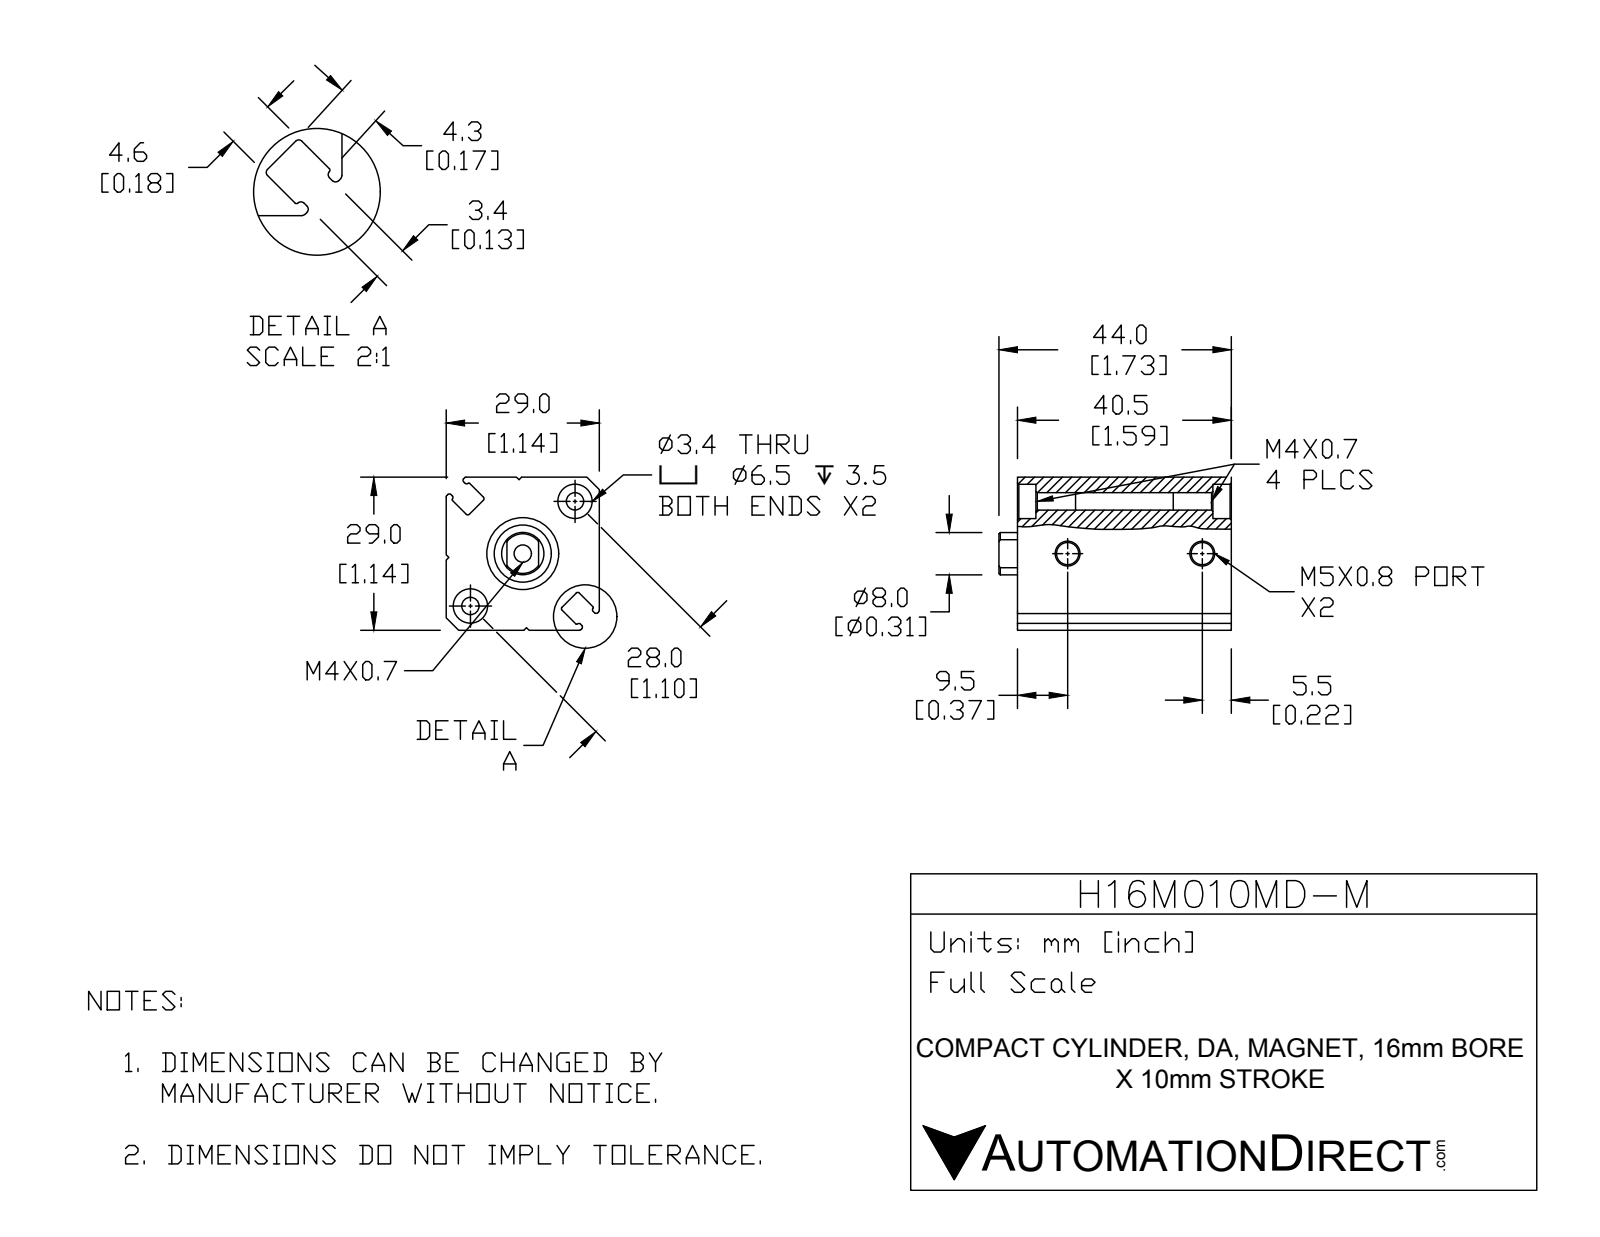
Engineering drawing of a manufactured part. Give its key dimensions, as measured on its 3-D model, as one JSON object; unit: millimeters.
{"part_name": "H16M010MD-M; H16M010MD-M-BODY; H16M010MD-M-PISTON", "step_written_by": "SolidWorks 2015 (CONFIG_CONTROL_DESIGN)", "units": "millimeters", "bodies": {"solids": 2, "faces": 128, "planar": 49, "cylindrical": 54, "other": 25}, "overall_size": [44, 29, 29], "volume_mm3": 28361, "surface_area_mm2": 12019, "round_holes": [[3.3, 3], [4.2, 2], [6.5, 2], [8, 1], [13.6, 1], [16, 1]], "round_bosses_or_shafts": [[10.8, 1]], "partial_cylinders_radius": [[0.4, 16], [0.2, 4]], "face_to_face_distances": [29, 40.5, 4, 36.5, 4.6, 16.53, 21.13, 24.84, 20.2, 16.2], "hole_center_spacings": [14, 25.5, 28]}
